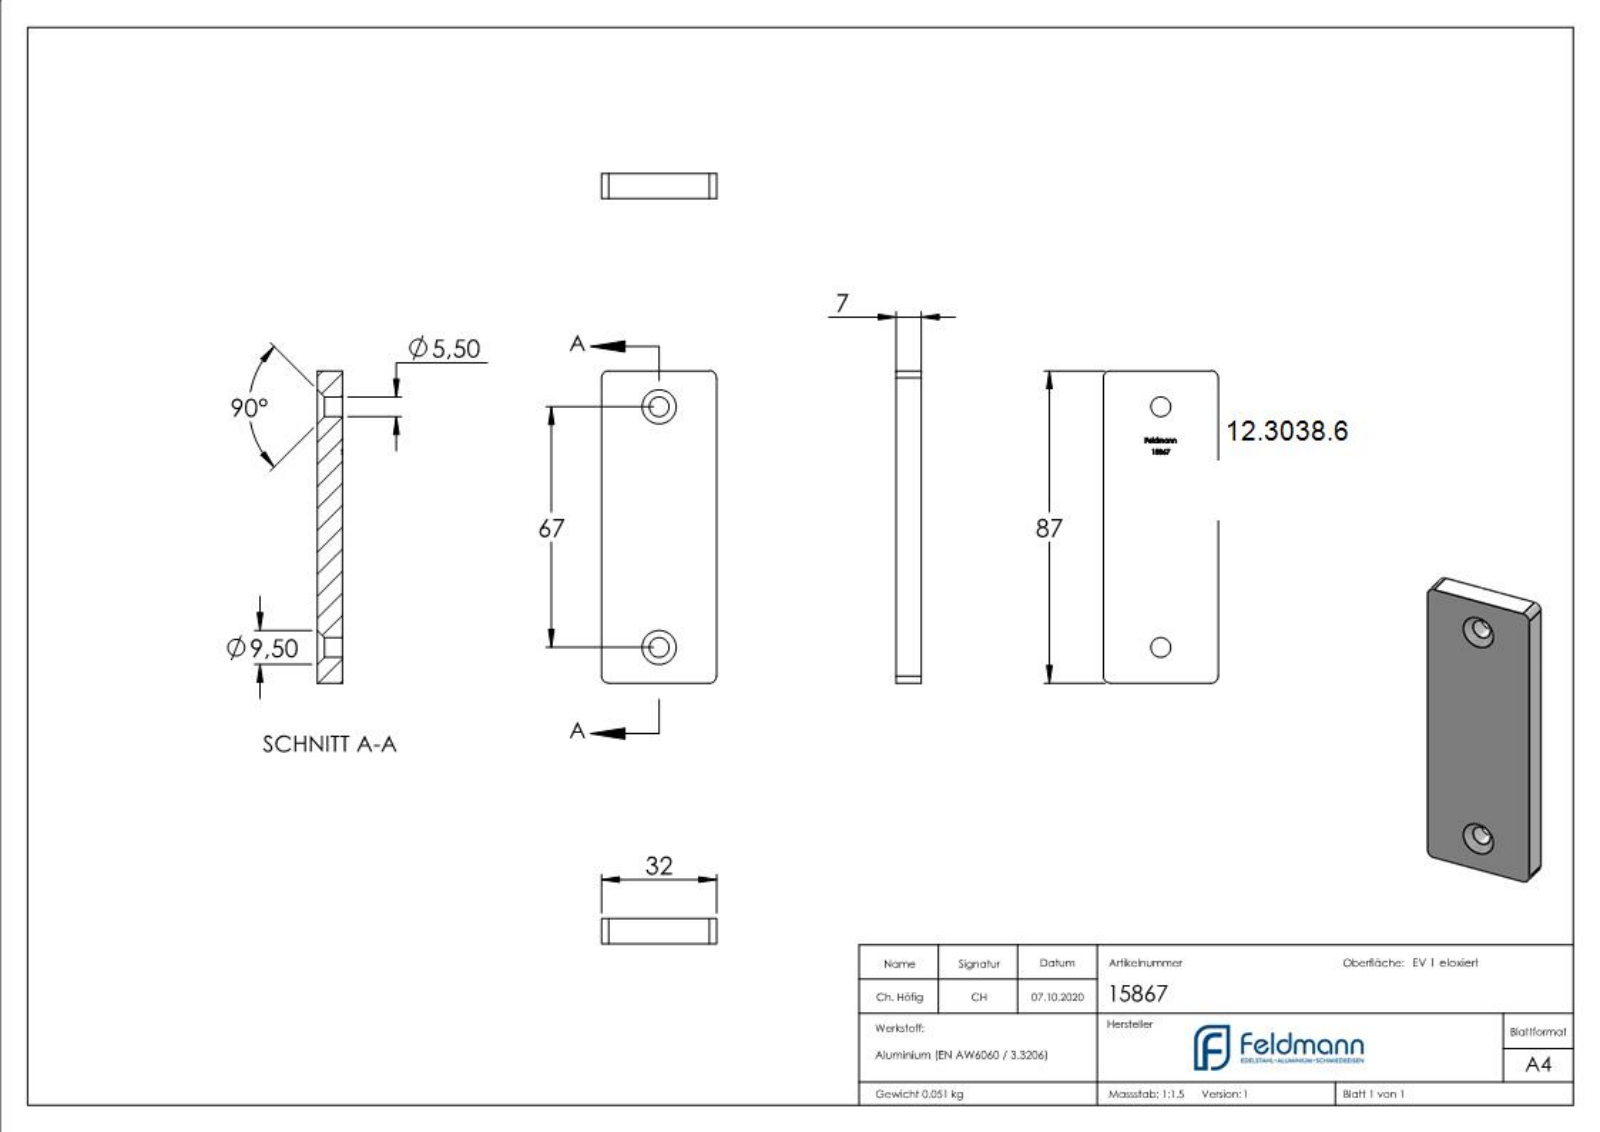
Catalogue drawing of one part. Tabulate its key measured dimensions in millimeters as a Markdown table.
| quantity | value |
| --- | --- |
| part name | AMF Schliessblech Konfig Teil1; 15867; AMF Schliessblech Konfig Teil1_15867 |
| STEP written by | SolidWorks 2018 (CONFIG_CONTROL_DESIGN) |
| units | millimeters |
| bodies | 1 solid, 194 faces (100 planar, 8 cylindrical, 86 other) |
| overall size | 87 × 32 × 7 |
| volume | 19 045 mm³ |
| surface area | 7 327 mm² |
| round holes (diameter × count) | 5.5 × 2 |
| partial cylindrical surfaces (radius × count) | 2 × 4 |
| main face-to-face distances | 7, 32, 87, 6.9, 0.39, 2.97, 2.02, 2.19, 1.08, 1.12 |
| hole center spacings | 67 |
